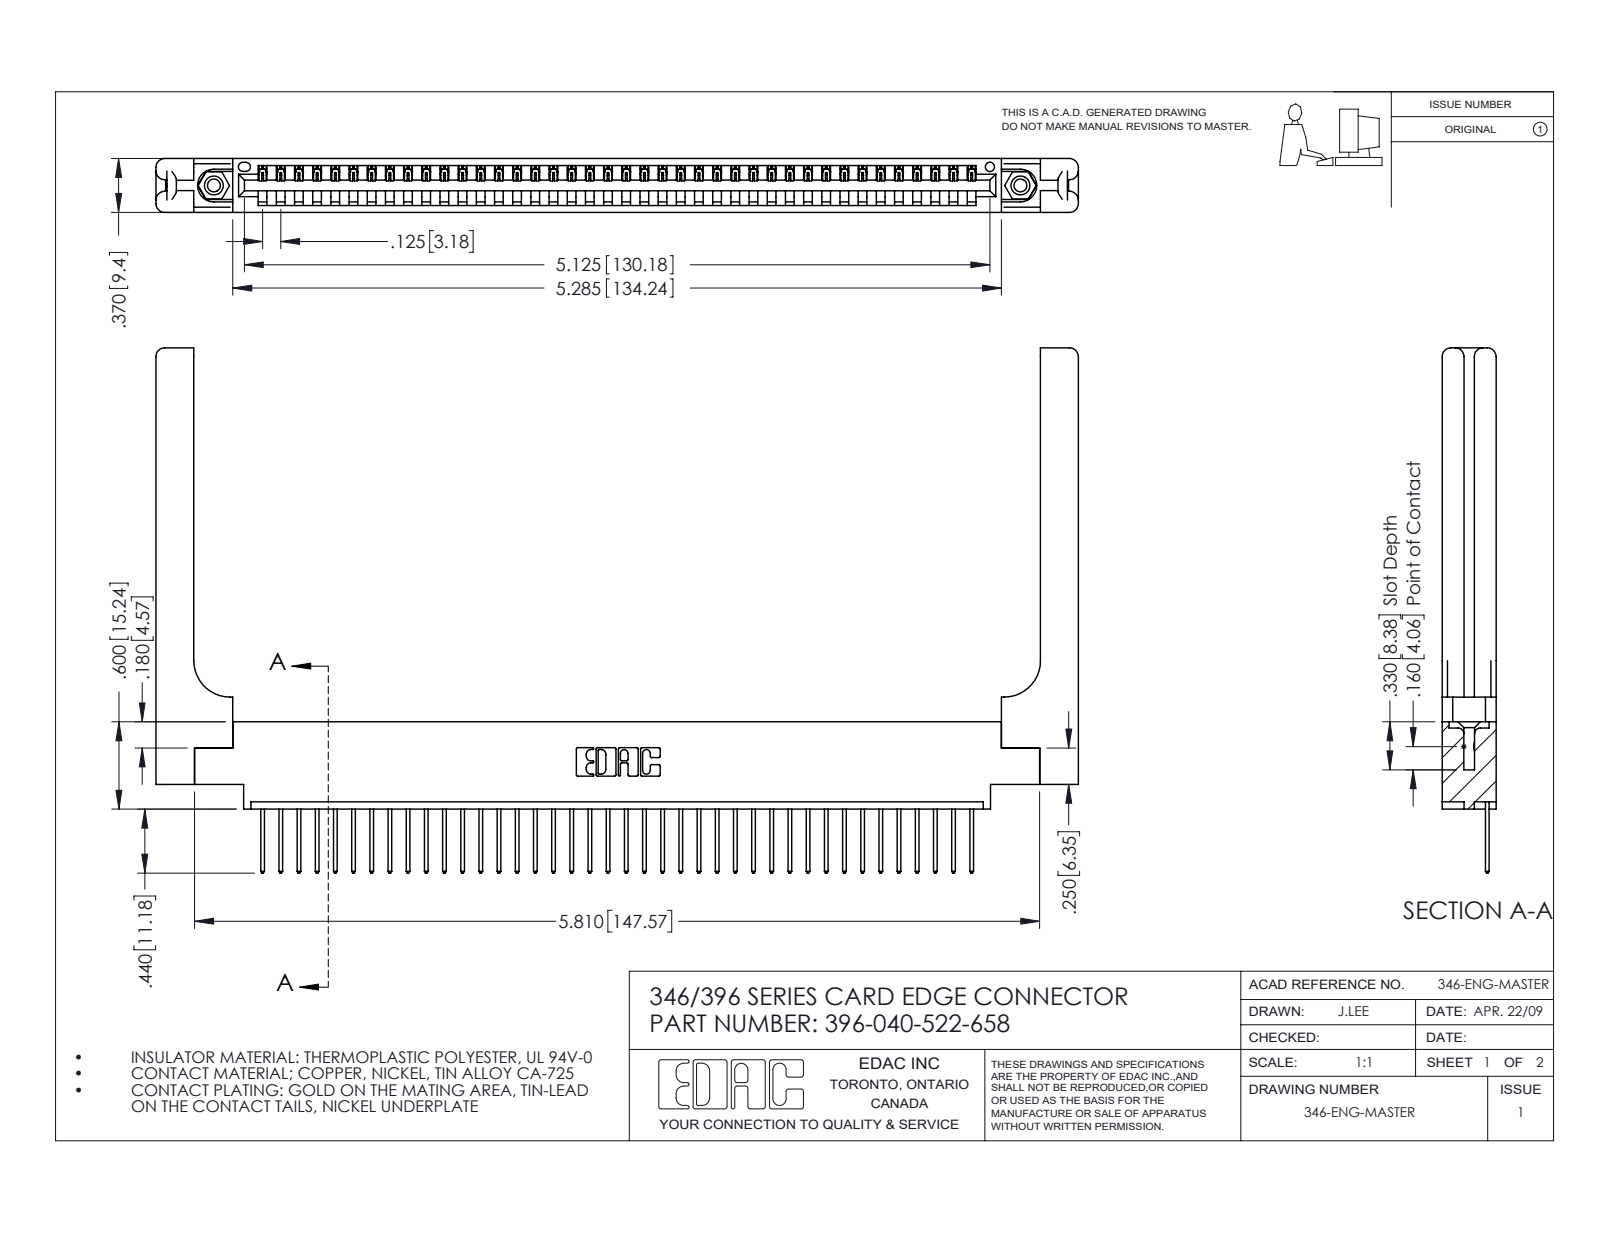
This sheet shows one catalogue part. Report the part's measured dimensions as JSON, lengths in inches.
{"part_name": "346-220-058_345-220-058; 345-292-001_345-293-122; 396-040-522-658; 345-250-001_345-250-001-102 (+1 more)", "step_written_by": "SolidWorks 2016 (CONFIG_CONTROL_DESIGN)", "units": "inches", "bodies": {"solids": 45, "faces": 2702, "planar": 1828, "cylindrical": 814, "other": 60}, "overall_size": [6.341, 3.61, 0.37], "volume_in3": 1.39, "surface_area_in2": 38.01, "round_holes": [[0.089, 2], [0.125, 2], [0.156, 2], [0.064, 1]], "round_bosses_or_shafts": [[0.155, 2]], "partial_cylinders_radius": [[0.006, 80], [0.01, 80], [0.01, 22], [0.06, 16], [0.007, 6], [0.031, 6], [0.026, 3], [0.03, 2]], "face_to_face_distances": [0.37, 0.048, 0.322, 0.072, 0.148, 0.15, 0.25, 0.298, 0.025, 0.222], "hole_center_spacings": [0.246, 5.336, 5.545]}
